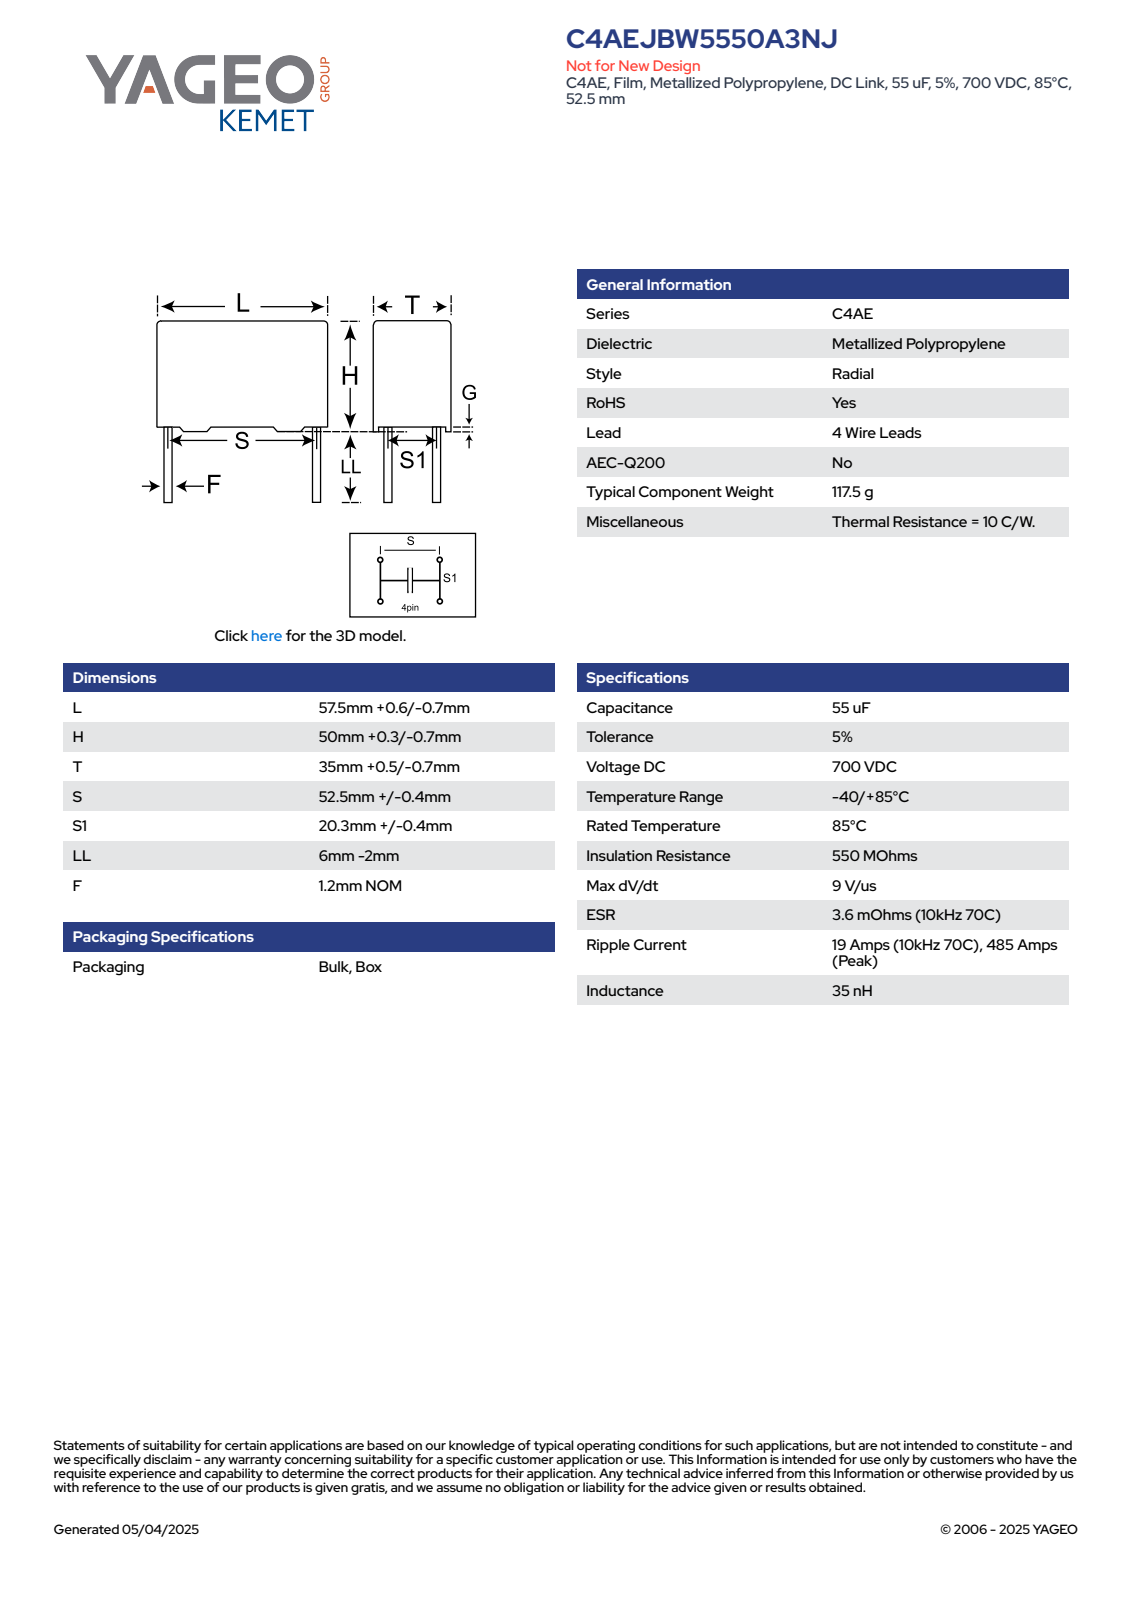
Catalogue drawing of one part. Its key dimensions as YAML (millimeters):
part_name: "CFP_RB4G_57.5X50X35_L58.1H50.3T35.5S52.5S120.3LL4F1.2G0.5"
step_written_by: "SolidWorks 2014 (AUTOMOTIVE_DESIGN)"
units: millimeters
bodies: {solids: 4, faces: 91, planar: 83, cylindrical: 8, other: 0}
overall_size: [58.1, 54.3, 35.51]
volume: 102771
surface_area: 13706
round_bosses_or_shafts:
  - {diameter: 1.2, count: 4}
face_to_face_distances: [35.5, 49.8, 58.1, 0.5, 50.3, 2, 33.5, 31.5, 4, 4.5]
